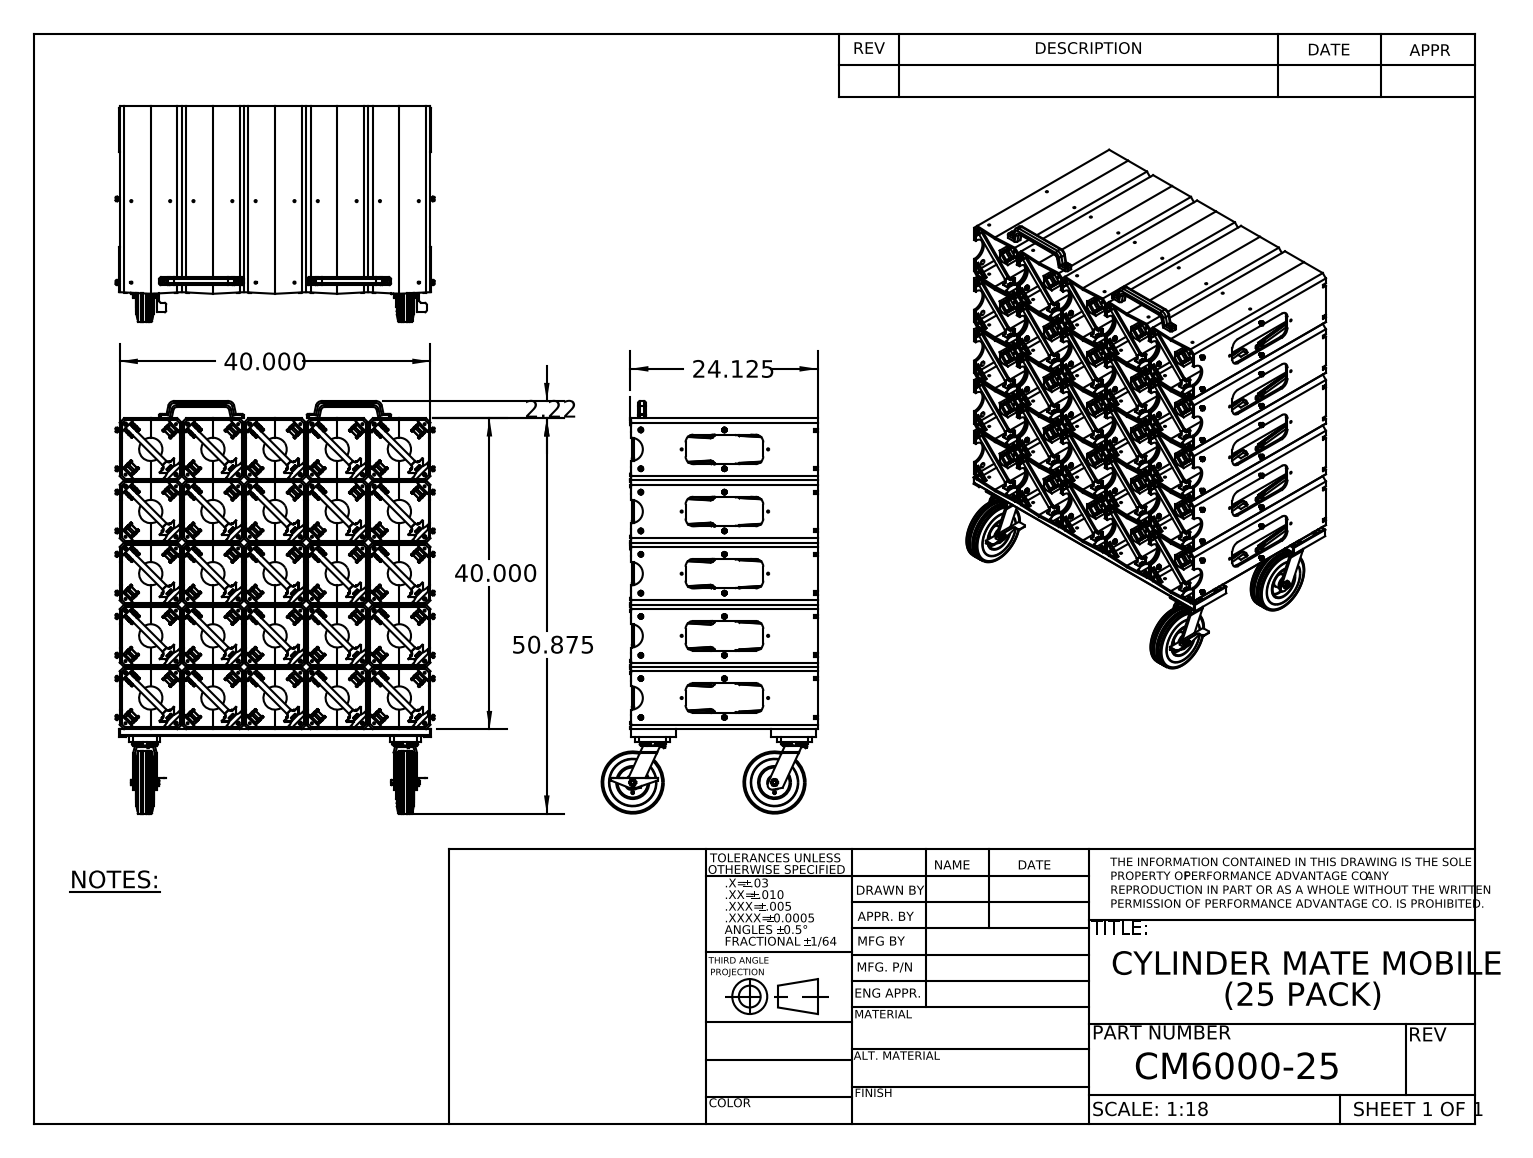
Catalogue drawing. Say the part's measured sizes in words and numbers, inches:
The part is named "CM6000-25; 7020x24(cmate mobile)_40; A416S x 5.750_SHORT; 9SF8X3-SB (+8 more)". Its 3-D file was written by "SolidWorks 2010 (CONFIG_CONTROL_DESIGN)". It is 890 solids with 42989 faces: 15097 planar, 11416 cylindrical and 16476 other. Overall it measures 53.093 by 41 by 27.803 inches. Its volume is 7 048 cubic inches and its surface area 47 865 square inches. Round holes: 100 of diameter 0.26, 79 of diameter 0.266, 20 of diameter 0.201, 4 of diameter 0.343, 4 of diameter 0.733, 3 of diameter 0.5, 2 of diameter 0.446, 2 of diameter 0.625, 2 of diameter 0.687, 2 of diameter 0.75, 2 of diameter 1.126, 2 of diameter 1.188. Round bosses or shafts: 50 of diameter 0.437, 50 of diameter 0.25, 25 of diameter 3, 20 of diameter 0.585, 4 of diameter 3.4, 4 of diameter 2.1, 4 of diameter 1, 4 of diameter 0.312. Partial cylindrical surfaces (rounded edges, fillets, slot ends): 2412 of radius 0.094, 1880 of radius 0.016, 410 of radius 0.031, 400 of radius 0.296, 400 of radius 0.452, 270 of radius 0.062, 225 of radius 0.125, 200 of radius 0.1. The main face-to-face distances are 8, 16, 0.25, 7.75, 24, 8.25, 15.75, 23.75, 16.25, 7.5. The hole center spacings are 8, 16, 6.5, 24, 5, 10.308, 3, 13.
